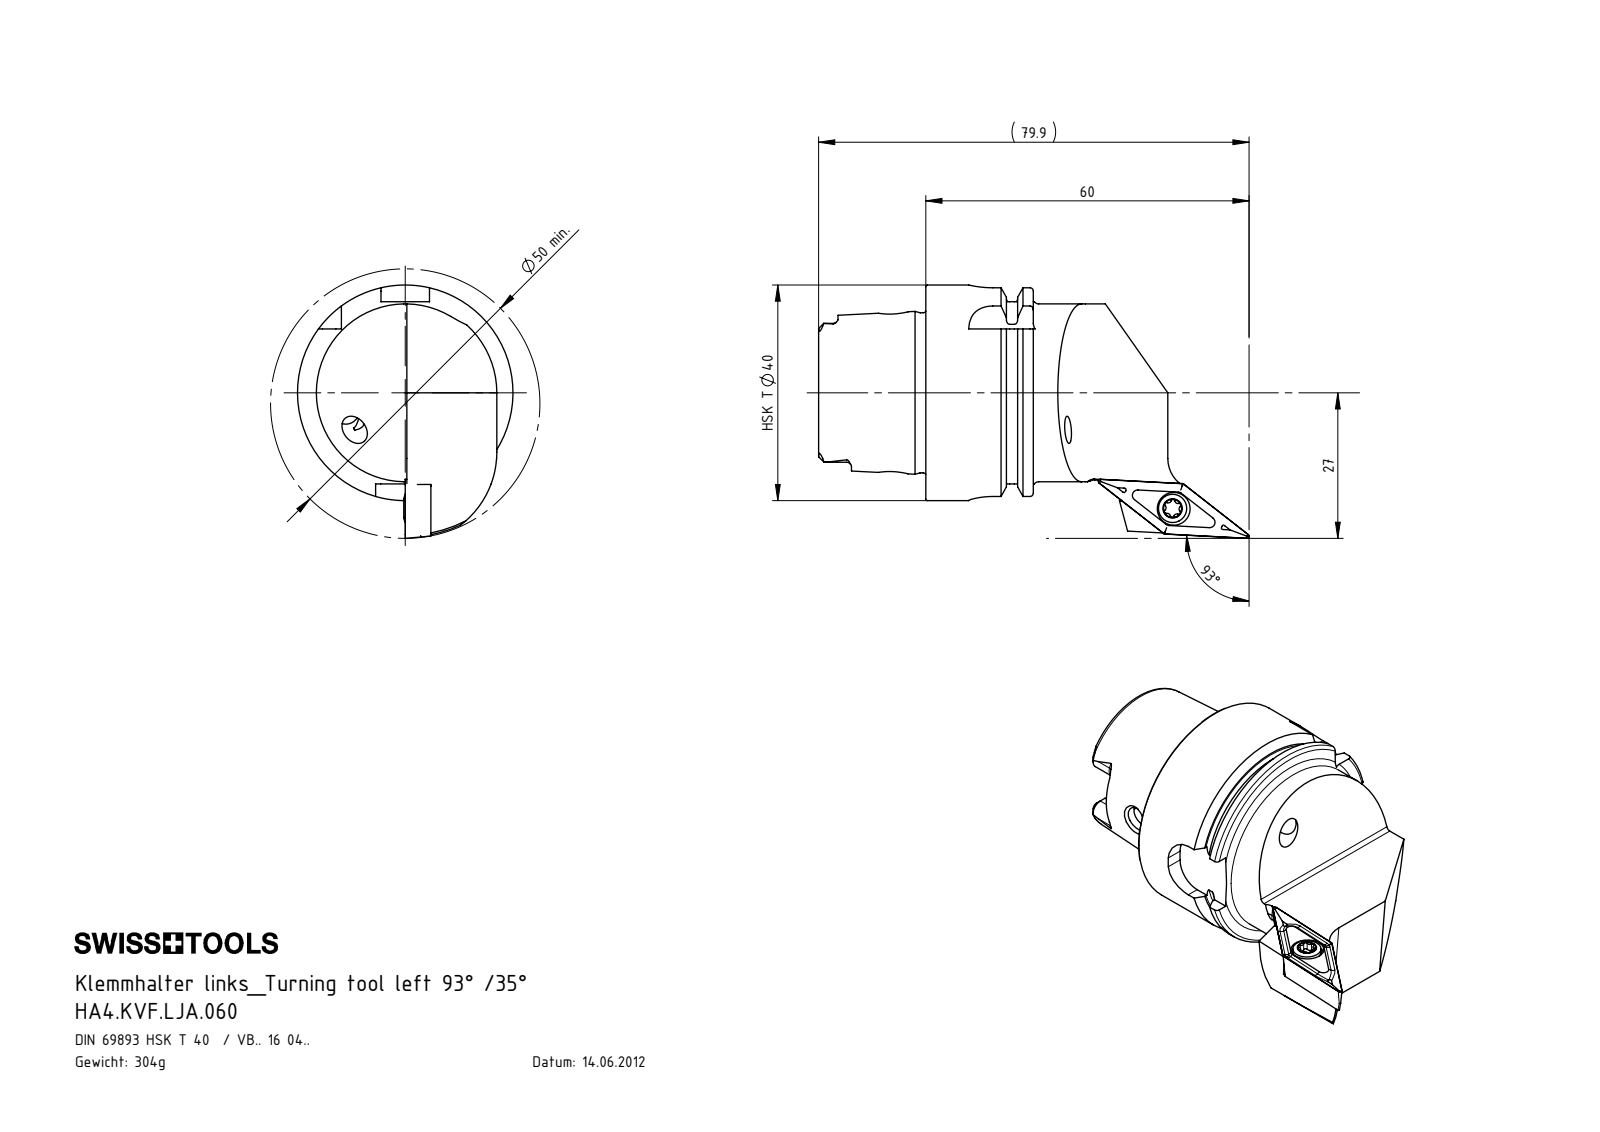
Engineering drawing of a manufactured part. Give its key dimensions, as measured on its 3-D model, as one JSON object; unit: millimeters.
{"part_name": "VBMT160404; WCB-ER2.001.009_A; HA4.KVF.LJA.060; HA4-KVF.LJA.060_A_Weichbearbeitung", "step_written_by": "SolidWorks 2017 (AUTOMOTIVE_DESIGN)", "units": "millimeters", "bodies": {"solids": 3, "faces": 288, "planar": 80, "cylindrical": 89, "other": 119}, "overall_size": [79.9, 47, 40], "volume_mm3": 38203, "surface_area_mm2": 13469, "round_holes": [[4.2, 2], [5, 2], [3.3, 1], [4.4, 1], [4.6, 1], [6.1, 1], [10, 1], [11, 1], [12.5, 1], [21, 1], [25.5, 1]], "round_bosses_or_shafts": [[40, 1], [34.75, 1], [33, 1], [29.71, 1], [5.25, 1], [4, 1]], "partial_cylinders_radius": [[0.34, 6], [0.59, 6], [0.9, 6], [1.88, 4], [4.5, 4], [0.15, 2], [17, 2], [0.8, 1]], "face_to_face_distances": [4.46, 7.95, 19.95, 12, 19.9, 27.85, 39.85, 35.7, 15.8, 7.85], "hole_center_spacings": [44.33, 44.55]}
